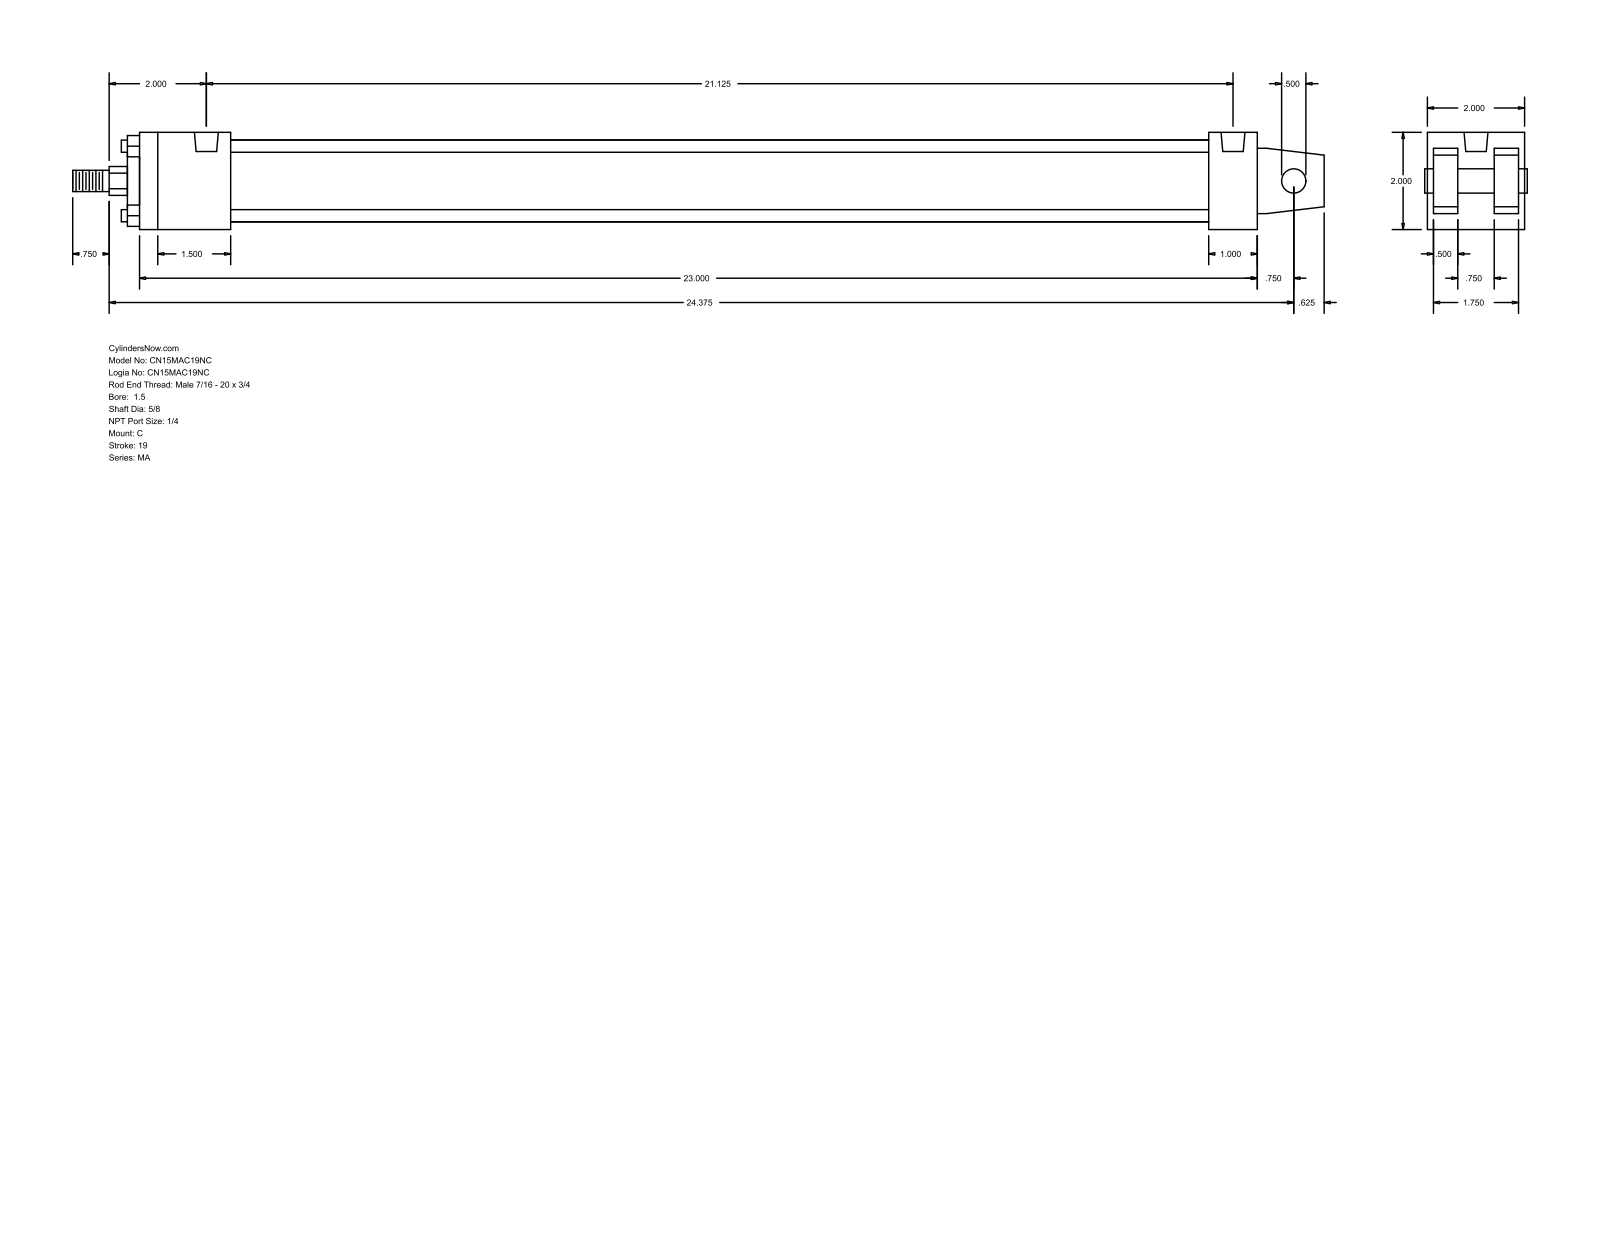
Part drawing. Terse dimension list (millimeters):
name: MA_C__0150_0.625
written by: GSSL Pune (CONFIG_CONTROL_DESIGN)
unit: mm
bodies: 0 solids, 103 faces (76 planar, 27 cylindrical, 0 other)
size: 654.05 × 50.8 × 50.8
holes: 4× ⌀7.94, 2× ⌀12.49
bosses: 4× ⌀6.35, 1× ⌀42.93, 1× ⌀28.57, 1× ⌀15.88, 1× ⌀12.7, 1× ⌀11.11
rounds: 1× R7.54
face distances: 50.8, 12.7, 34.93, 15.87, 3.17, 47.63, 31.76, 584.2, 558.79, 25.41
hole spacings: 536.58
